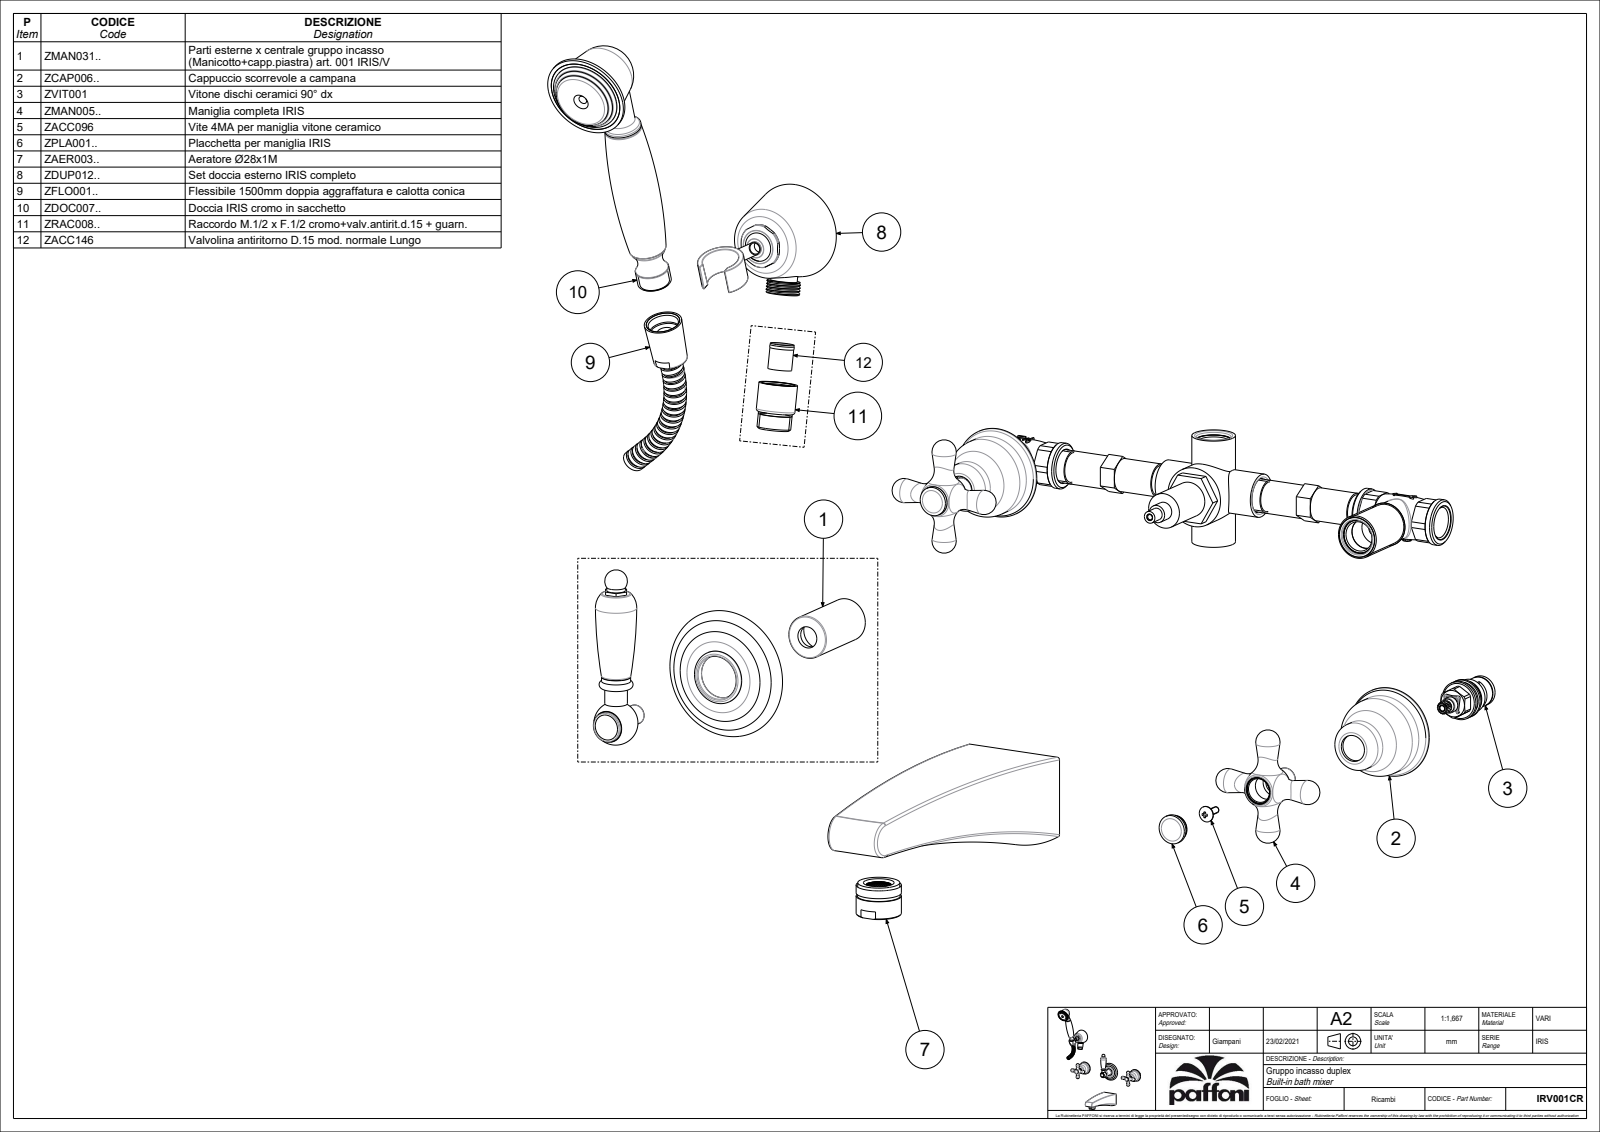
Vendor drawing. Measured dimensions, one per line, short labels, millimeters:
name: IRV001CR
written by: CREO PARAMETRIC BY PTC INC, 2020044 (CONFIG_CONTROL_DESIGN)
unit: mm
bodies: 5 solids, 439 faces (70 planar, 82 cylindrical, 287 other)
size: 477.78 × 369.09 × 200.5
volume: 897 822 mm³; area: 144 957 mm²
holes: 1× ⌀14.5, 1× ⌀17
bosses: 3× ⌀28, 3× ⌀18, 2× ⌀55, 2× ⌀49, 2× ⌀21, 2× ⌀14, 1× ⌀53, 1× ⌀44
rounds: 6× R0.3, 1× R13.25, 1× R13.5, 1× R14.5
face distances: 40, 10, 6.01, 30, 2, 6.5, 46.5, 36.5, 12.5, 2.5
